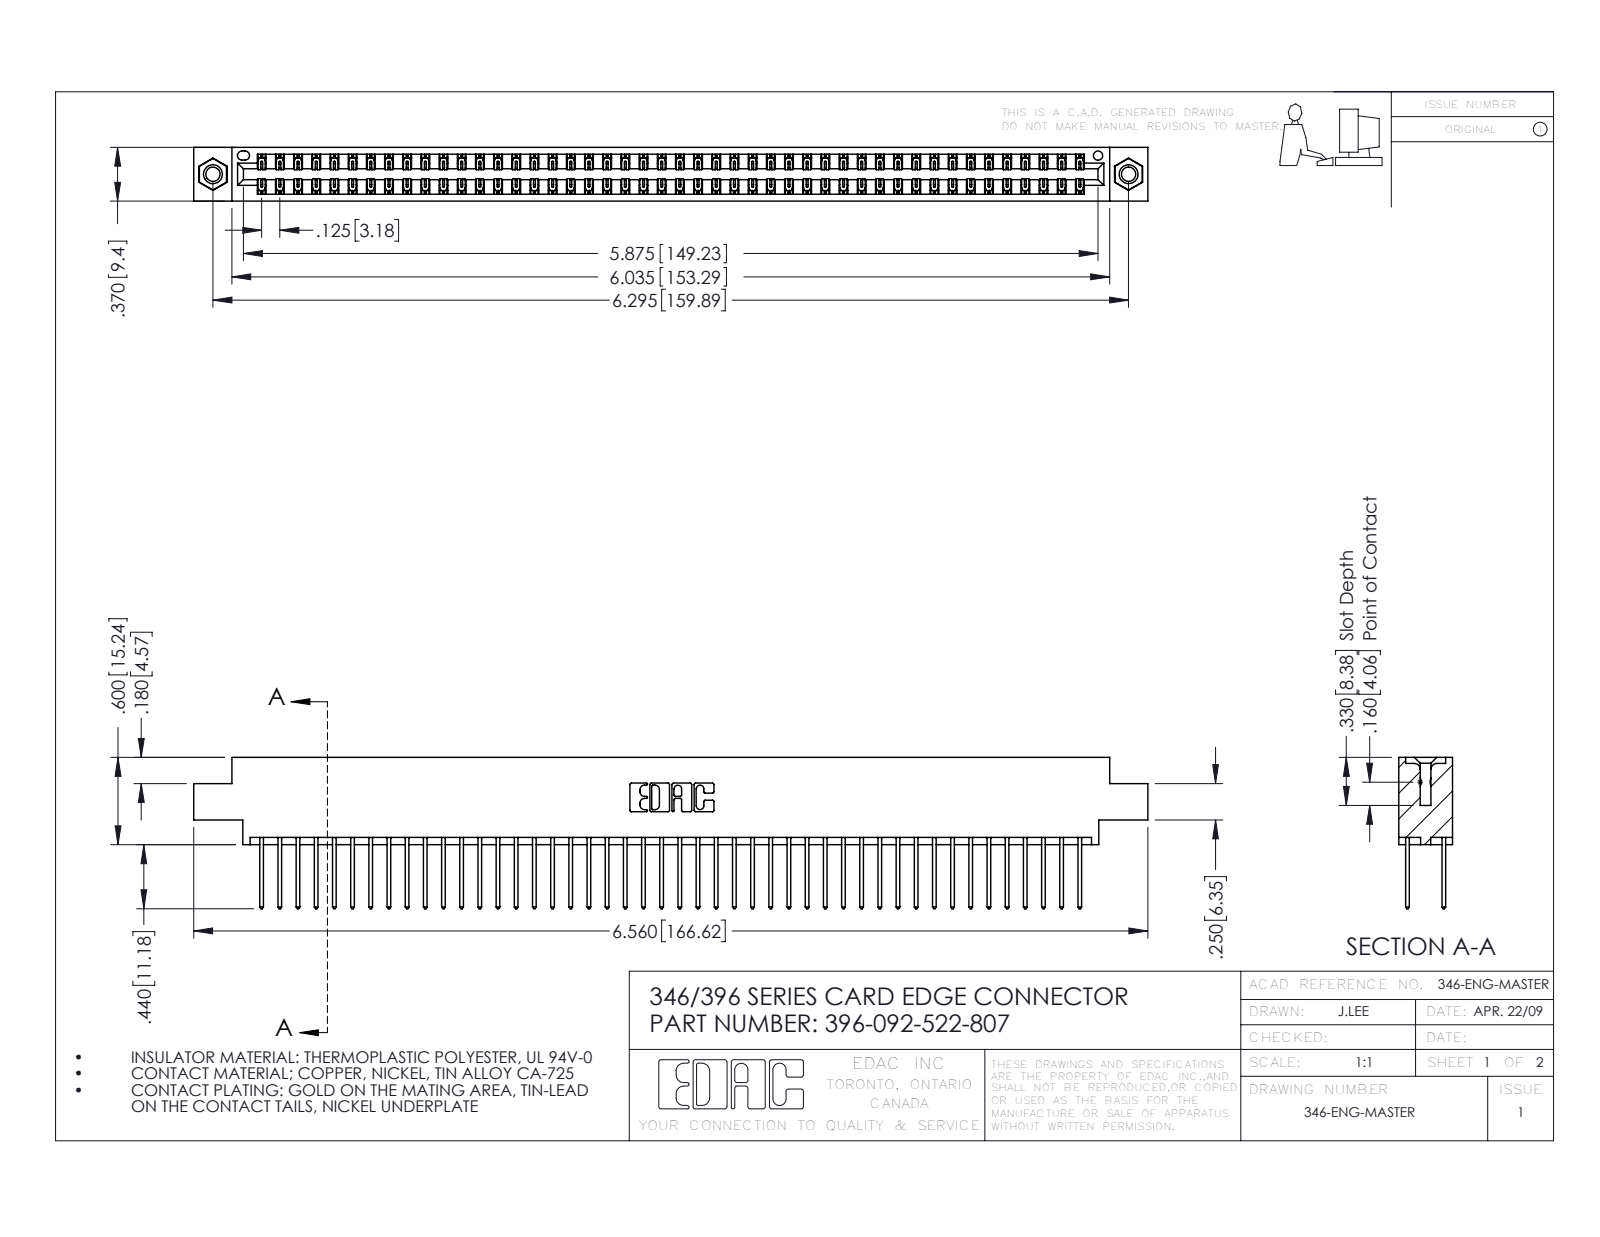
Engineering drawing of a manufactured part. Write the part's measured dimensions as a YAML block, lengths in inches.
part_name: "345-292-001_345-293-122; 396-092-522-807; 346 Part_0.170 Offset - 0.156 Dia-TI; 345-250-001_345-250-005-103"
step_written_by: "SolidWorks 2016 (CONFIG_CONTROL_DESIGN)"
units: inches
bodies: {solids: 95, faces: 4970, planar: 3332, cylindrical: 1622, other: 16}
overall_size: [6.56, 1.04, 0.37]
volume: 0.998
surface_area: 36.95
round_holes:
  - {diameter: 0.098, count: 2}
  - {diameter: 0.125, count: 2}
  - {diameter: 0.156, count: 2}
  - {diameter: 0.064, count: 1}
round_bosses_or_shafts:
  - {diameter: 0.155, count: 2}
partial_cylinders:
  - {radius: 0.006, count: 138}
  - {radius: 0.01, count: 92}
  - {radius: 0.01, count: 22}
  - {radius: 0.007, count: 6}
  - {radius: 0.031, count: 6}
  - {radius: 0.026, count: 3}
  - {radius: 0.014, count: 2}
  - {radius: 0.022, count: 2}
face_to_face_distances: [0.048, 0.322, 0.25, 0.37, 0.072, 0.298, 0.025, 0.275, 0.222, 0.148]
hole_center_spacings: [0.246, 6.086, 6.295]
